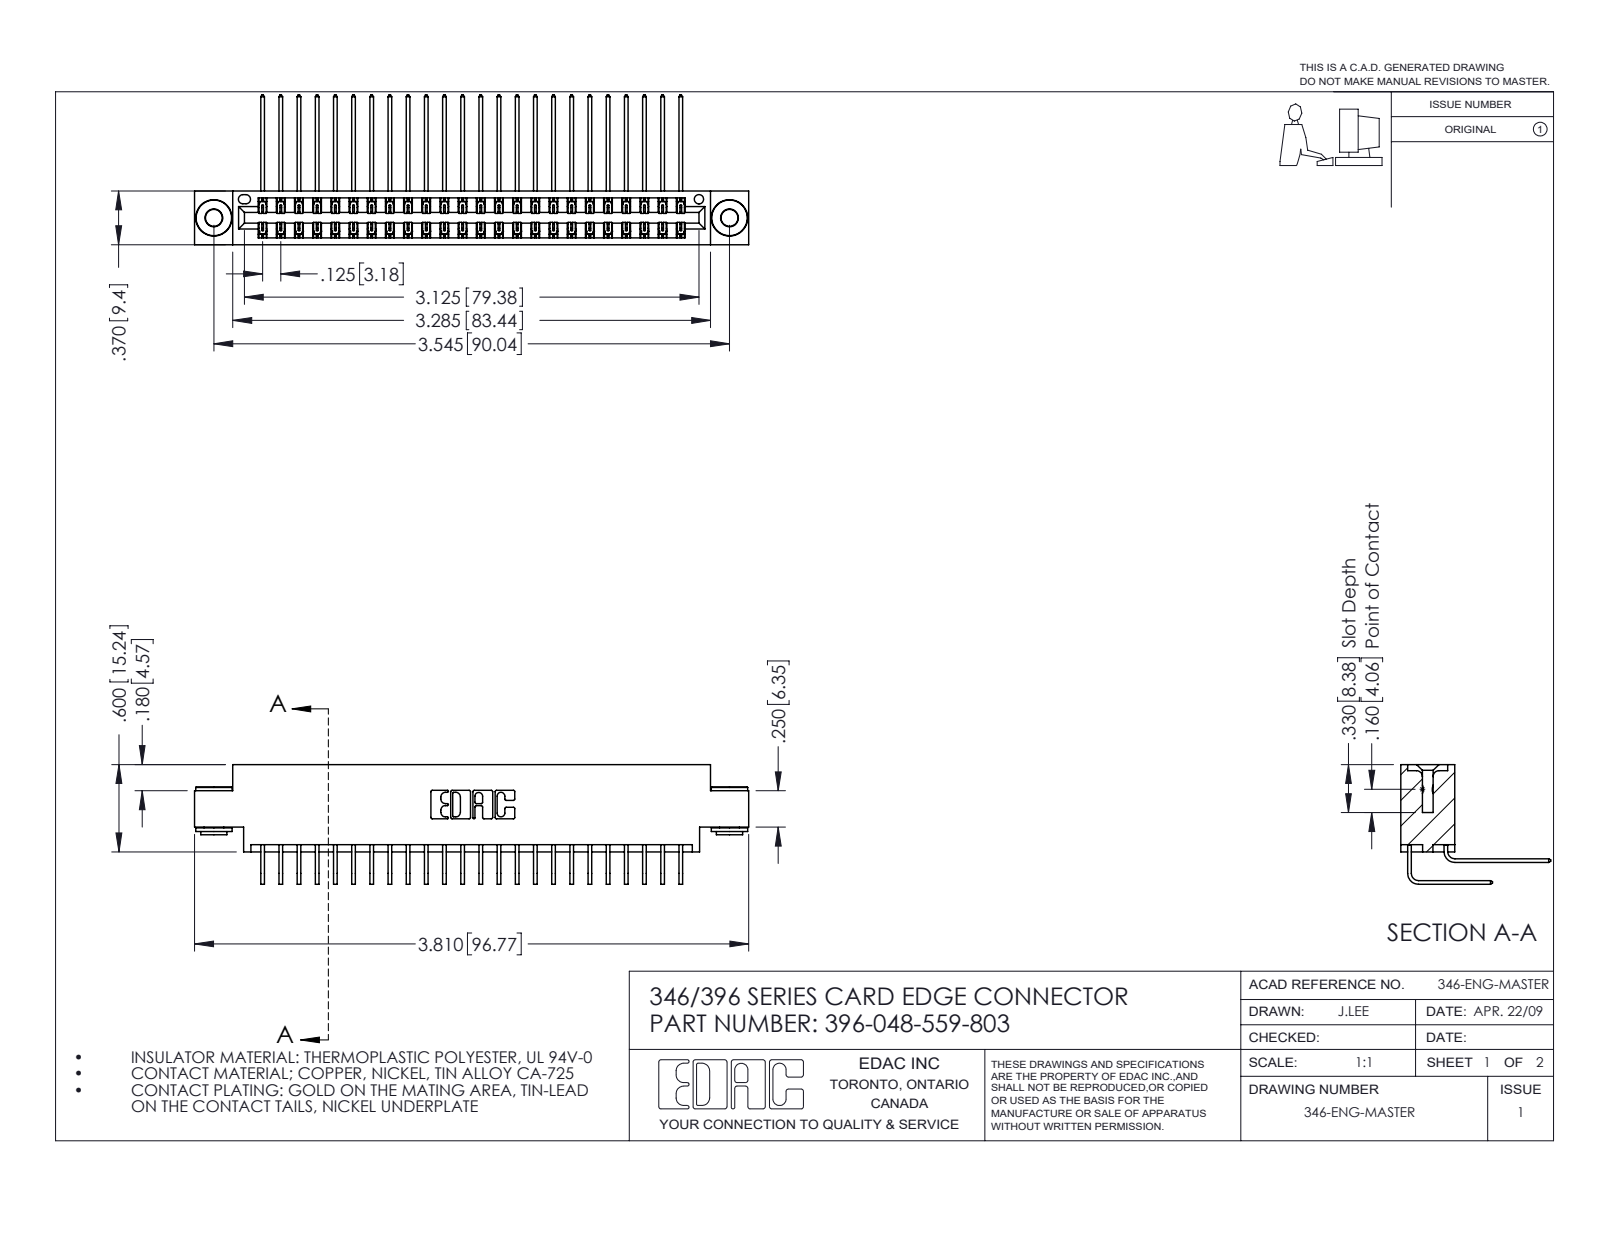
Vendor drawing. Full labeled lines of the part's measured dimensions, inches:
Part name (STEP PRODUCT): 345-292-001_559 Tail - 2; 396-048-559-803; 345-250-002_345-250-002-102; 346 Part_0.170 Offset - 0.156 Dia-TH (+1 more)
STEP written by: SolidWorks 2016 (CONFIG_CONTROL_DESIGN)
Units: inches
Bodies: 51 solids, 2756 faces (1866 planar, 882 cylindrical, 8 other)
Overall size (bounding box): 3.81 × 1.03 × 0.823
Volume: 0.576 in³ · Surface area: 22.34 in²
Round holes (diameter × count): ⌀0.116 ×2, ⌀0.156 ×2, ⌀0.064 ×1
Round bosses / shafts (diameter × count): ⌀0.25 ×2, ⌀0.18 ×2, ⌀0.136 ×2
Partial cylindrical surfaces — rounded edges, fillets, slot ends (radius × count): R0.006 ×72, R0.01 ×22, R0.007 ×6, R0.031 ×6, R0.026 ×3, R0.014 ×2, R0.022 ×2, R0.024 ×2
Main face-to-face distances: 0.048, 0.322, 0.025, 0.37, 0.25, 0.072, 0.298, 0.275, 0.15, 0.148
Hole centre spacings: 0.246, 3.337, 3.545
